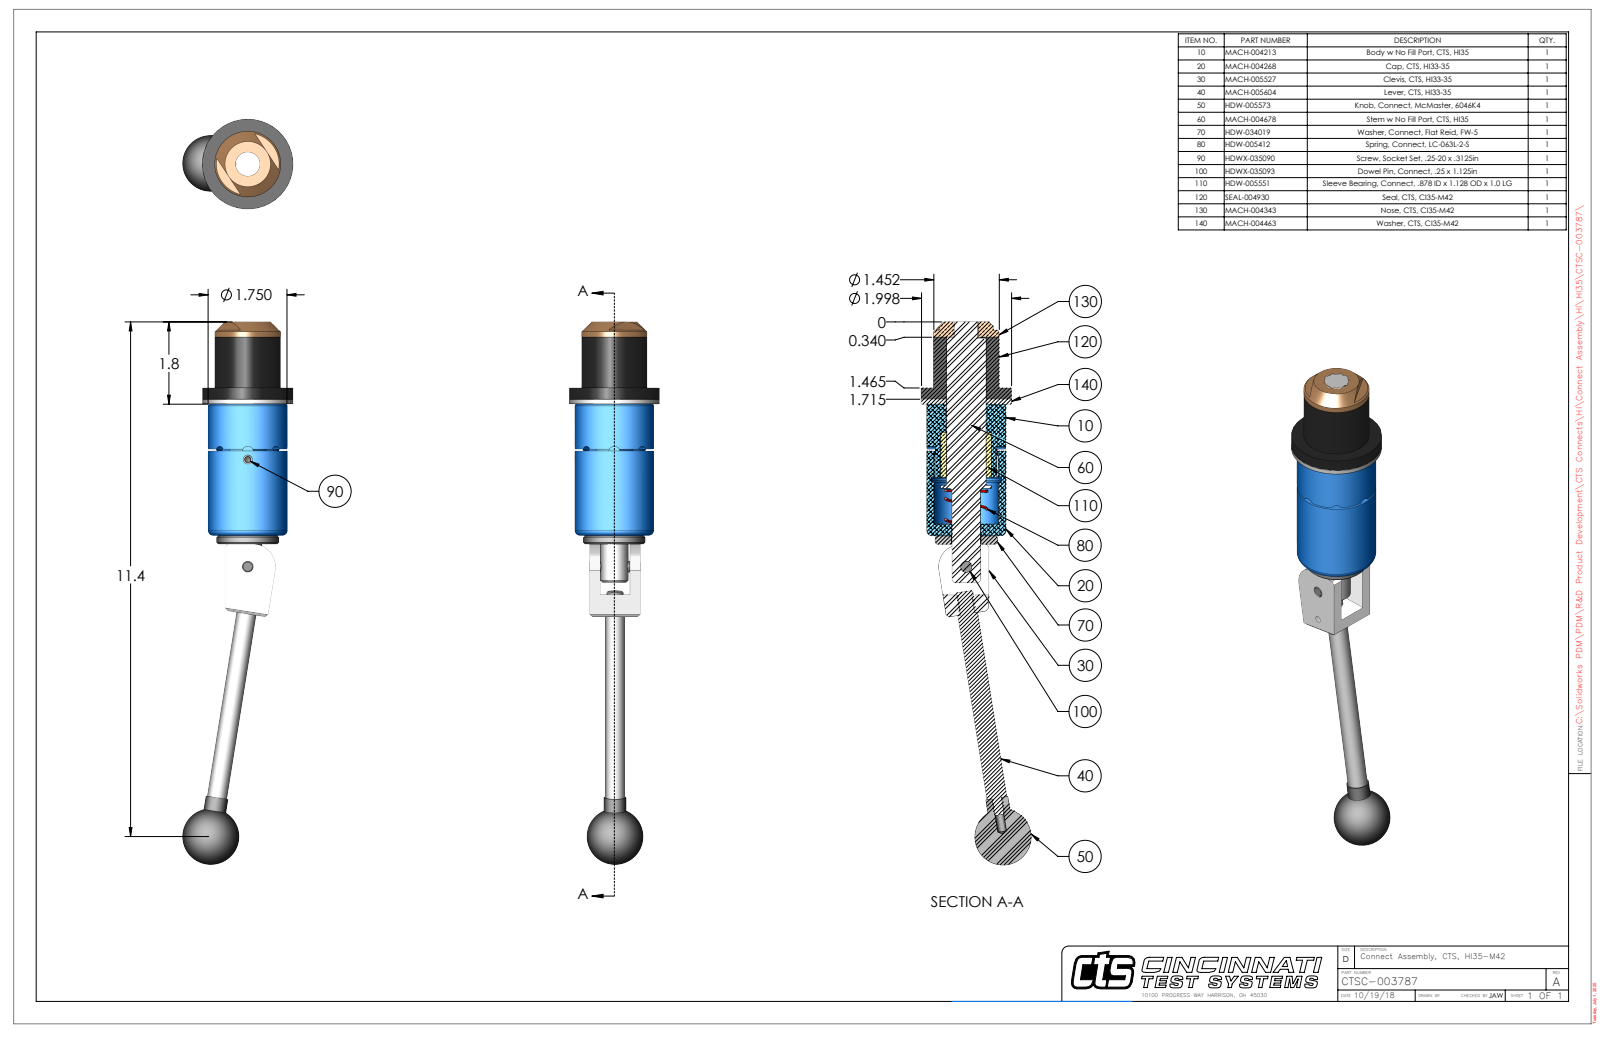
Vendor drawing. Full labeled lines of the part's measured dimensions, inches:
Part name (STEP PRODUCT): CTSC-003787
STEP written by: SolidWorks 2023 (AUTOMOTIVE_DESIGN)
Units: inches
Bodies: 9 solids, 248 faces (91 planar, 99 cylindrical, 58 other)
Overall size (bounding box): 12.039 × 2.436 × 1.998
Volume: 12.84 in³ · Surface area: 83.02 in²
Round holes (diameter × count): ⌀0.201 ×2, ⌀0.15 ×1, ⌀0.249 ×1, ⌀0.251 ×1, ⌀0.313 ×1, ⌀0.635 ×1, ⌀0.656 ×1, ⌀0.876 ×1, ⌀0.883 ×1, ⌀0.885 ×1, ⌀1.419 ×1, ⌀1.452 ×1
Round bosses / shafts (diameter × count): ⌀0.25 ×2, ⌀1.998 ×1, ⌀1.998 ×1, ⌀1.75 ×1, ⌀1.452 ×1, ⌀1.38 ×1, ⌀0.871 ×1, ⌀0.869 ×1
Partial cylindrical surfaces — rounded edges, fillets, slot ends (radius × count): R0.125 ×4, R0.029 ×2, R0.5 ×1, R0.695 ×1, R0.83 ×1
Main face-to-face distances: 0.11, 1.375, 1.485, 4.402, 3.027, 2.917, 1.125, 0.25, 0.36, 3.277
Hole centre spacings: 0.74, 2.376, 3.116
